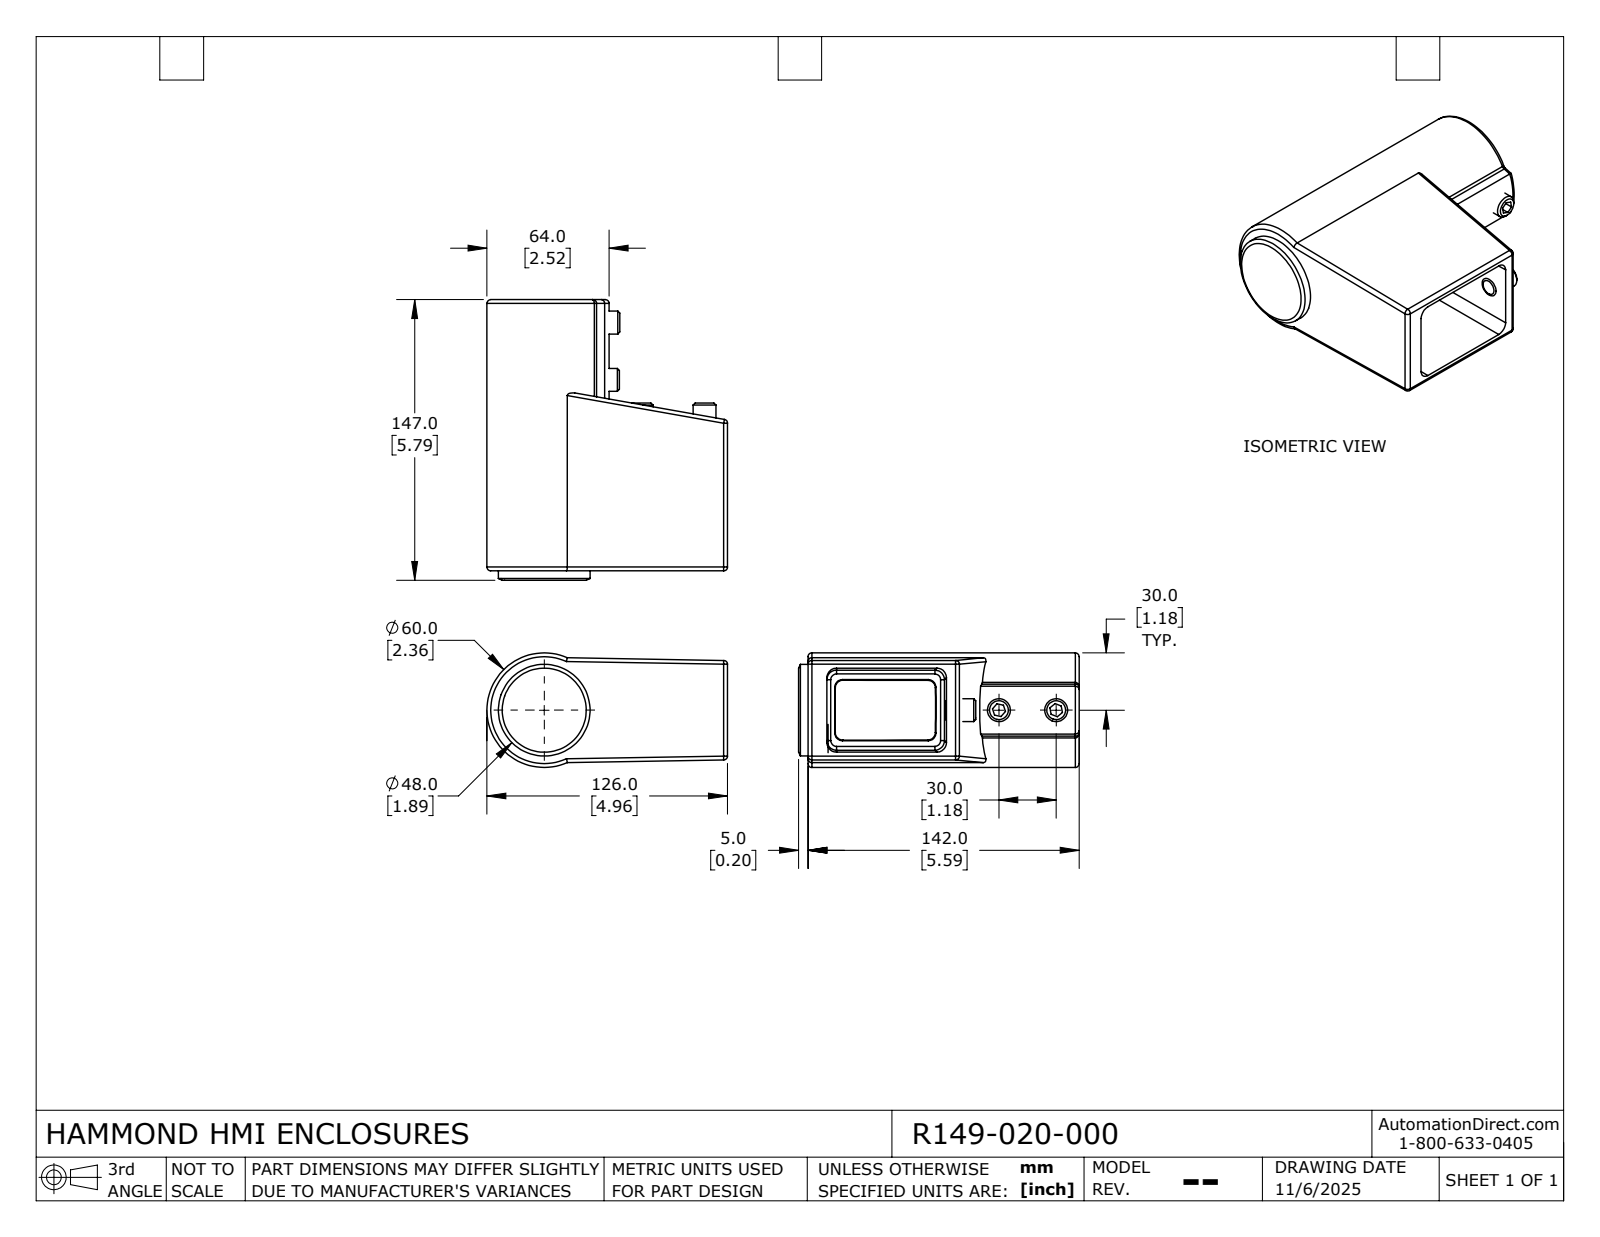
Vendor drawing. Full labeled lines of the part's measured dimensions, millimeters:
Part name (STEP PRODUCT): R149-020-000
STEP written by: SolidWorks 2024 (AUTOMOTIVE_DESIGN)
Units: millimetres
Bodies: 8 solids, 175 faces (89 planar, 50 cylindrical, 36 other)
Overall size (bounding box): 343 × 314 × 60
Volume: 508 389 mm³ · Surface area: 260 608 mm²
Round holes (diameter × count): ⌀10.11 ×4, ⌀40 ×1, ⌀45 ×1
Round bosses / shafts (diameter × count): ⌀12 ×4, ⌀60 ×1, ⌀48 ×1, ⌀42 ×1
Partial cylindrical surfaces — rounded edges, fillets, slot ends (radius × count): R2 ×20, R4 ×8, R5 ×4, R34 ×1
Main face-to-face distances: 3, 37, 57, 40, 34, 60, 54, 14.9, 71.9, 68.9
Hole centre spacings: 30, 33, 51, 84
